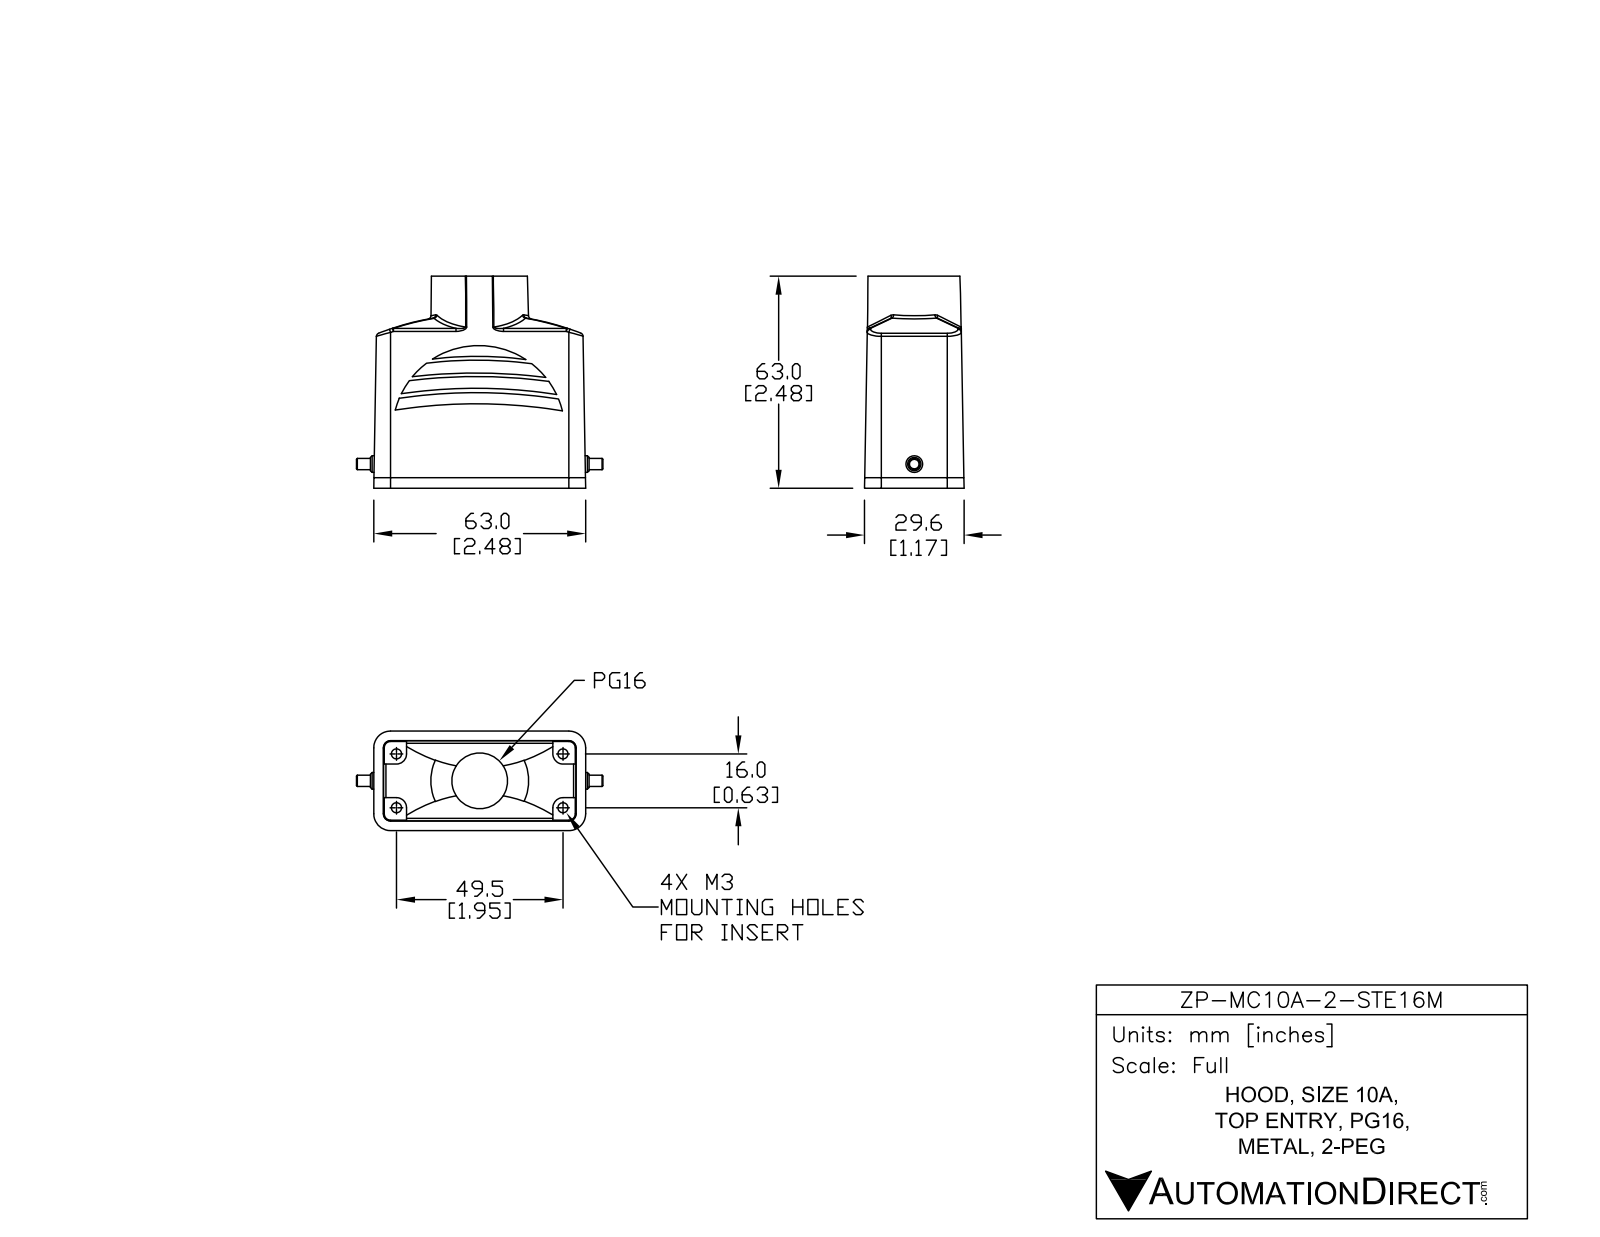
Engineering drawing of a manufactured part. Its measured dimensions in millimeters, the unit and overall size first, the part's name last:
Units: millimetres
Overall size (bounding box): 73.25 × 63.32 × 29.6
Round holes (diameter × count): ⌀3 ×4, ⌀16.55 ×1, ⌀21.25 ×1
Round bosses / shafts (diameter × count): ⌀4.95 ×1, ⌀3.35 ×1
Partial cylindrical surfaces — rounded edges, fillets, slot ends (radius × count): R1 ×4, R3 ×4, R25.65 ×2, R111.46 ×2, R124.56 ×2, R154.25 ×2, R155.71 ×2, R159.01 ×2
Main face-to-face distances: 2.85, 2.63, 2.62, 63.32, 10, 43.5, 14.6, 48.72, 50.12, 35.52
Hole centre spacings: 26.01, 16, 49.5, 52.02
Volume: 33 028 mm³ · Surface area: 22 095 mm²
Bodies: 1 solid, 208 faces (54 planar, 89 cylindrical, 65 other)
Part name (STEP PRODUCT): ZP-MC10A-2-STE16M
STEP written by: SolidWorks 2014 (AUTOMOTIVE_DESIGN)
